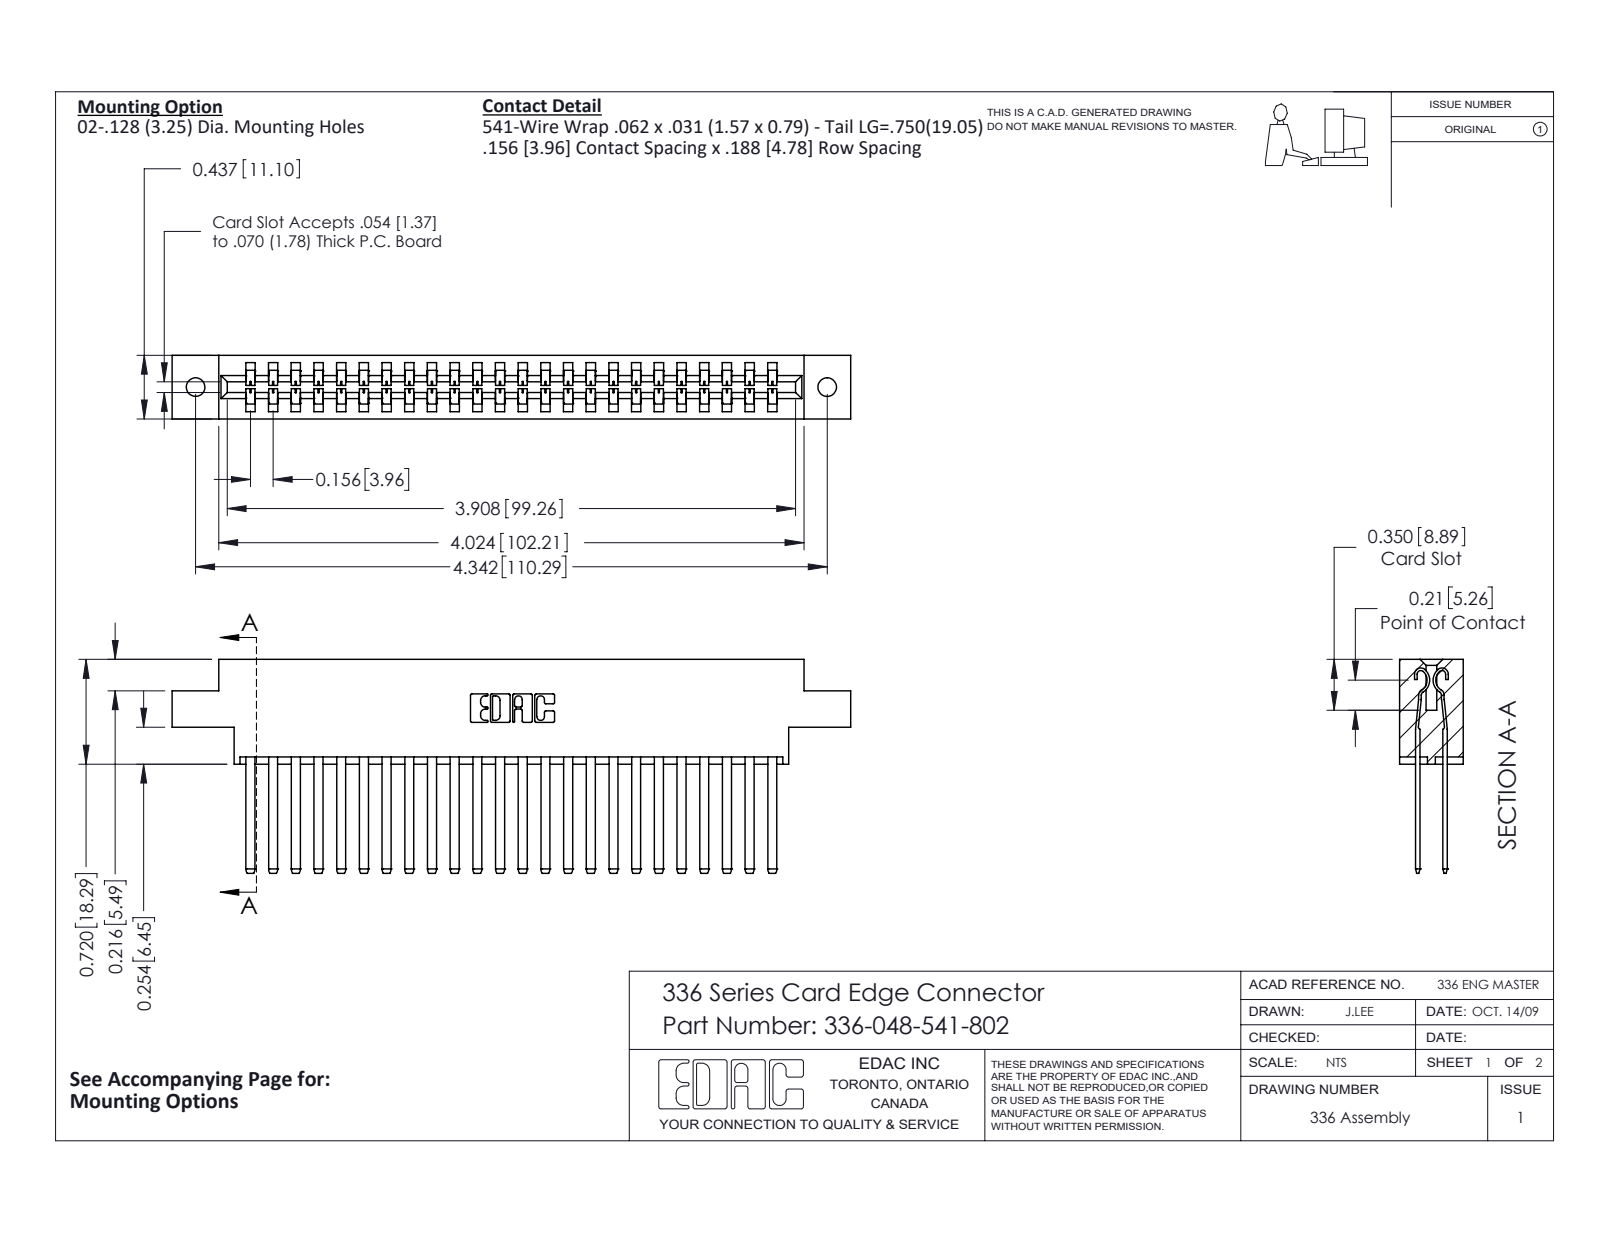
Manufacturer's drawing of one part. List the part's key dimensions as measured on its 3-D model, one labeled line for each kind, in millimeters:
Part name (STEP PRODUCT): 336-290-001_336-290-541; 336-048-541-802; 336 Part_Offset - .128 Dia
STEP written by: SolidWorks 2020 (CONFIG_CONTROL_DESIGN)
Units: millimetres
Bodies: 49 solids, 2134 faces (1322 planar, 812 cylindrical, 0 other)
Overall size (bounding box): 118.5 × 37.3 × 11.1
Volume: 17 530 mm³ · Surface area: 22 010 mm²
Round holes (diameter × count): ⌀3.3 ×2
Partial cylindrical surfaces — rounded edges, fillets, slot ends (radius × count): R0.1 ×96, R1.4 ×48, R0.3 ×22, R0.2 ×6, R0.8 ×6, R0.6 ×4, R1 ×4, R0.7 ×3
Main face-to-face distances: 4.8, 8.3, 3.6, 7.5, 2.8, 0.8, 11.1, 0.8, 4, 4.6
Hole centre spacings: 110.3
